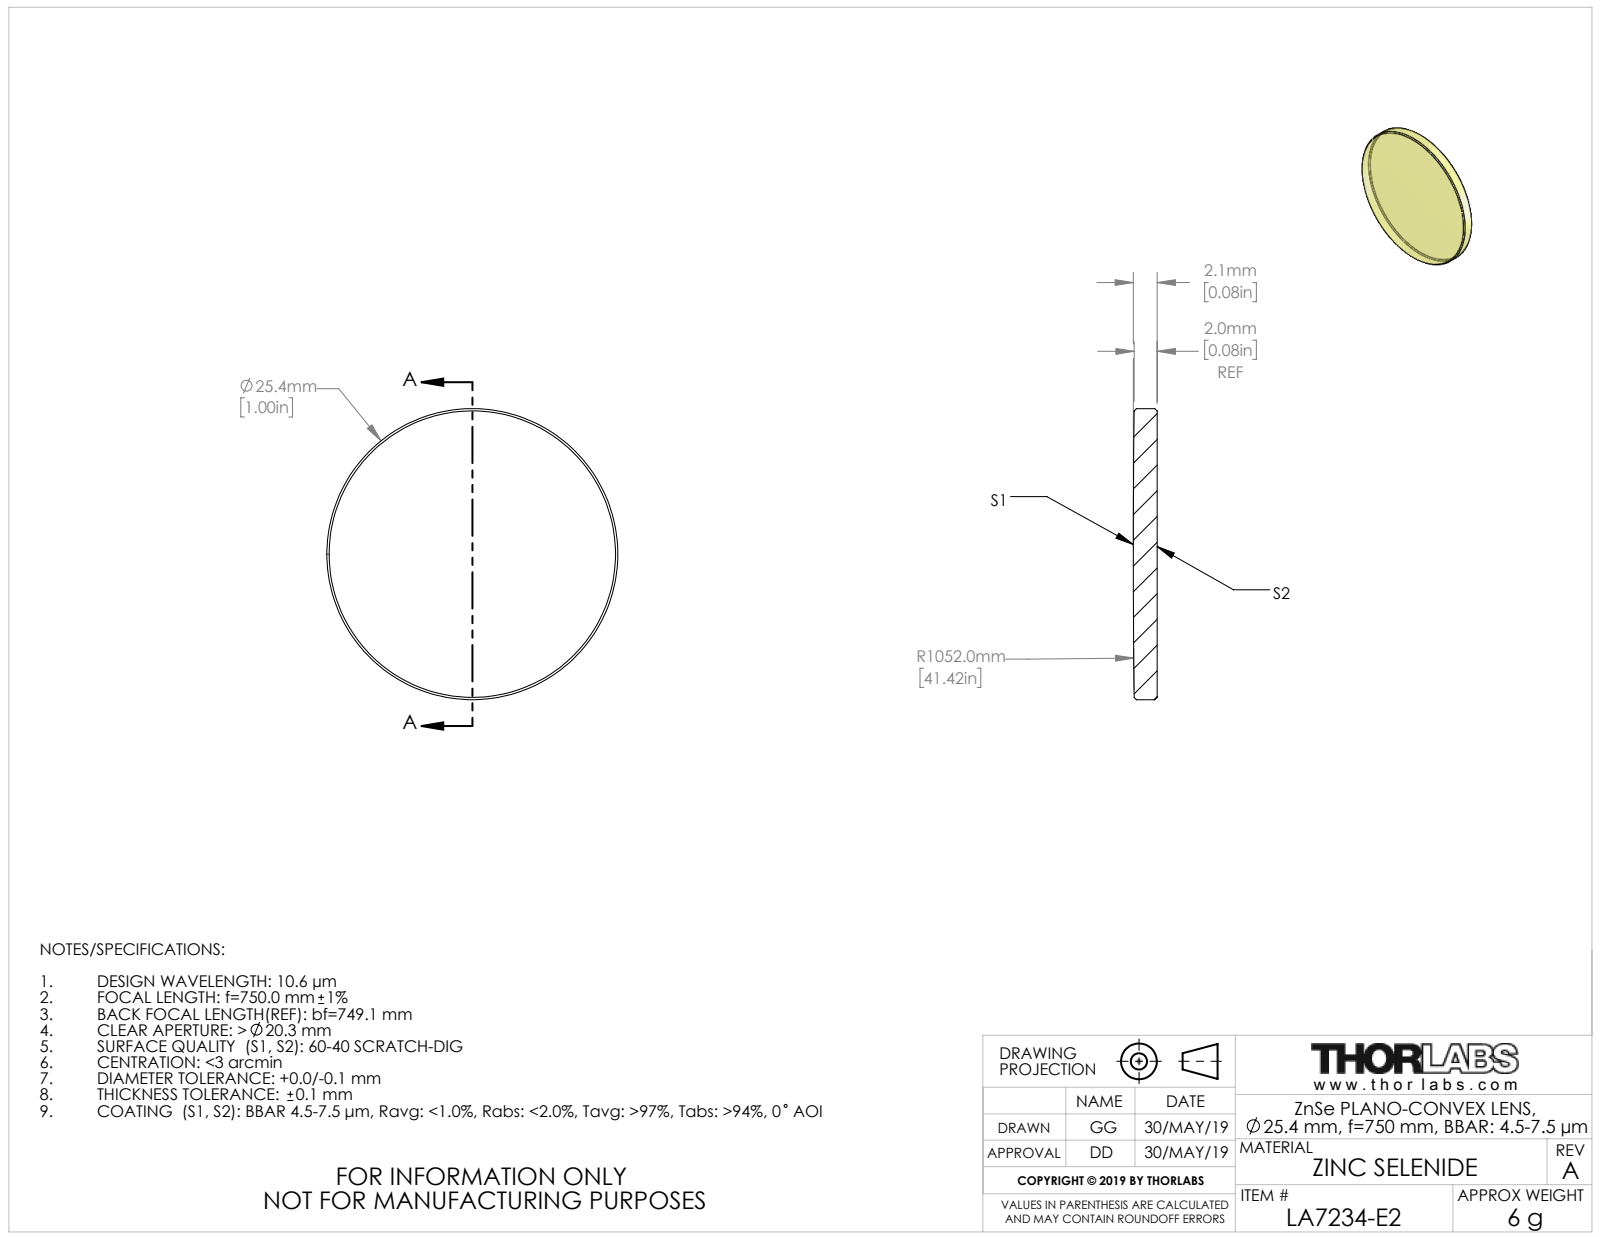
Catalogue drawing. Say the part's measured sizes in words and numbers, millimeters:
The part is named "TTN047617-E0W". Its 3-D file was written by "SolidWorks 2018 (CONFIG_CONTROL_DESIGN)". It is 1 solid with 9 faces: 1 planar, 2 cylindrical and 6 other. Overall it measures 25.4 by 25.4 by 2.08 millimeters. Its volume is 1 031 cubic millimeters and its surface area 1 155 square millimeters. Round bosses or shafts: 1 of diameter 25.4.
